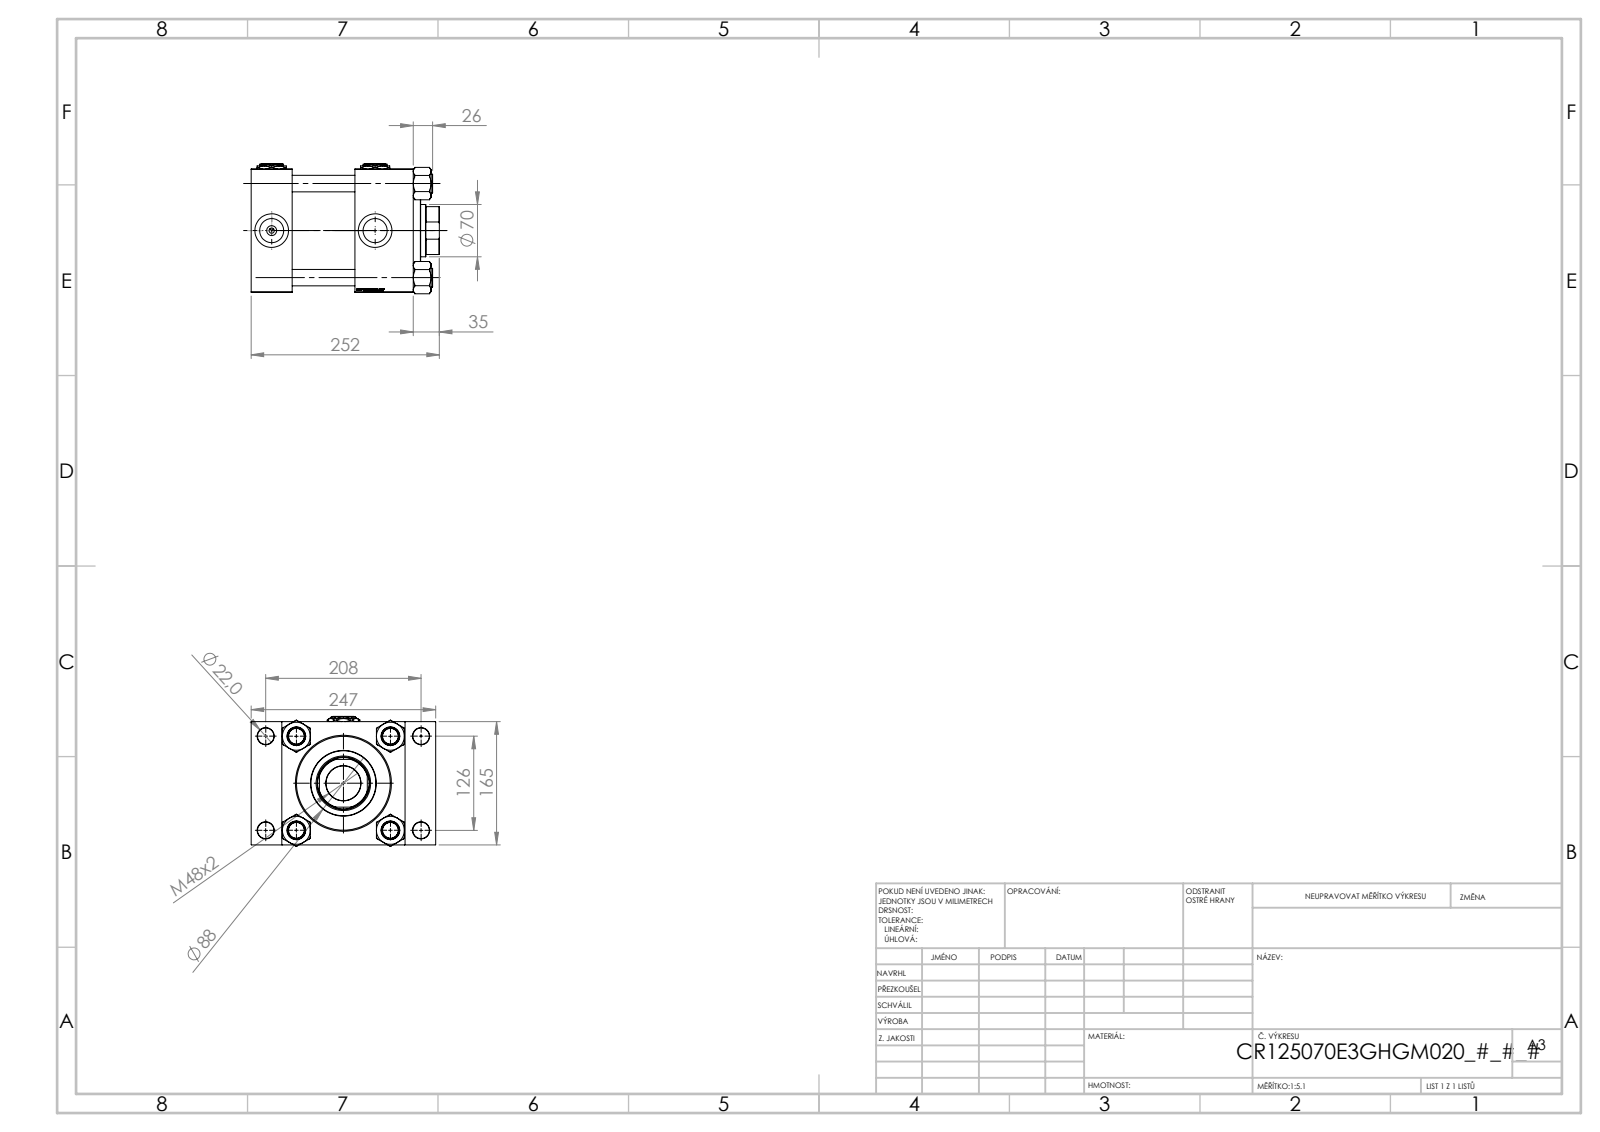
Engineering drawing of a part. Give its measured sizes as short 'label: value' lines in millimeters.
name: V215CR_E_Body; V215CR_VCP_E; NUT_M5_E; V215_VC_A (+2 more)
written by: SolidWorks 2019 (CONFIG_CONTROL_DESIGN)
unit: mm
bodies: 13 solids, 1290 faces (595 planar, 101 cylindrical, 594 other)
size: 252 × 247 × 174.07
volume: 5 258 000 mm³; area: 591 092 mm²
holes: 8× ⌀22, 4× ⌀32.24, 4× ⌀45, 3× ⌀7, 2× ⌀2.5, 1× ⌀46.5, 1× ⌀70, 1× ⌀73, 1× ⌀96, 1× ⌀125, 1× ⌀125.5
bosses: 4× ⌀25, 1× ⌀131, 1× ⌀88
rounds: 1× R34
face distances: 55, 165, 162, 217, 41, 78, 139, 84, 206, 188.3
hole spacings: 41.05, 62.98, 76.28, 89.02, 121.59, 125.9, 132.47, 139.02
